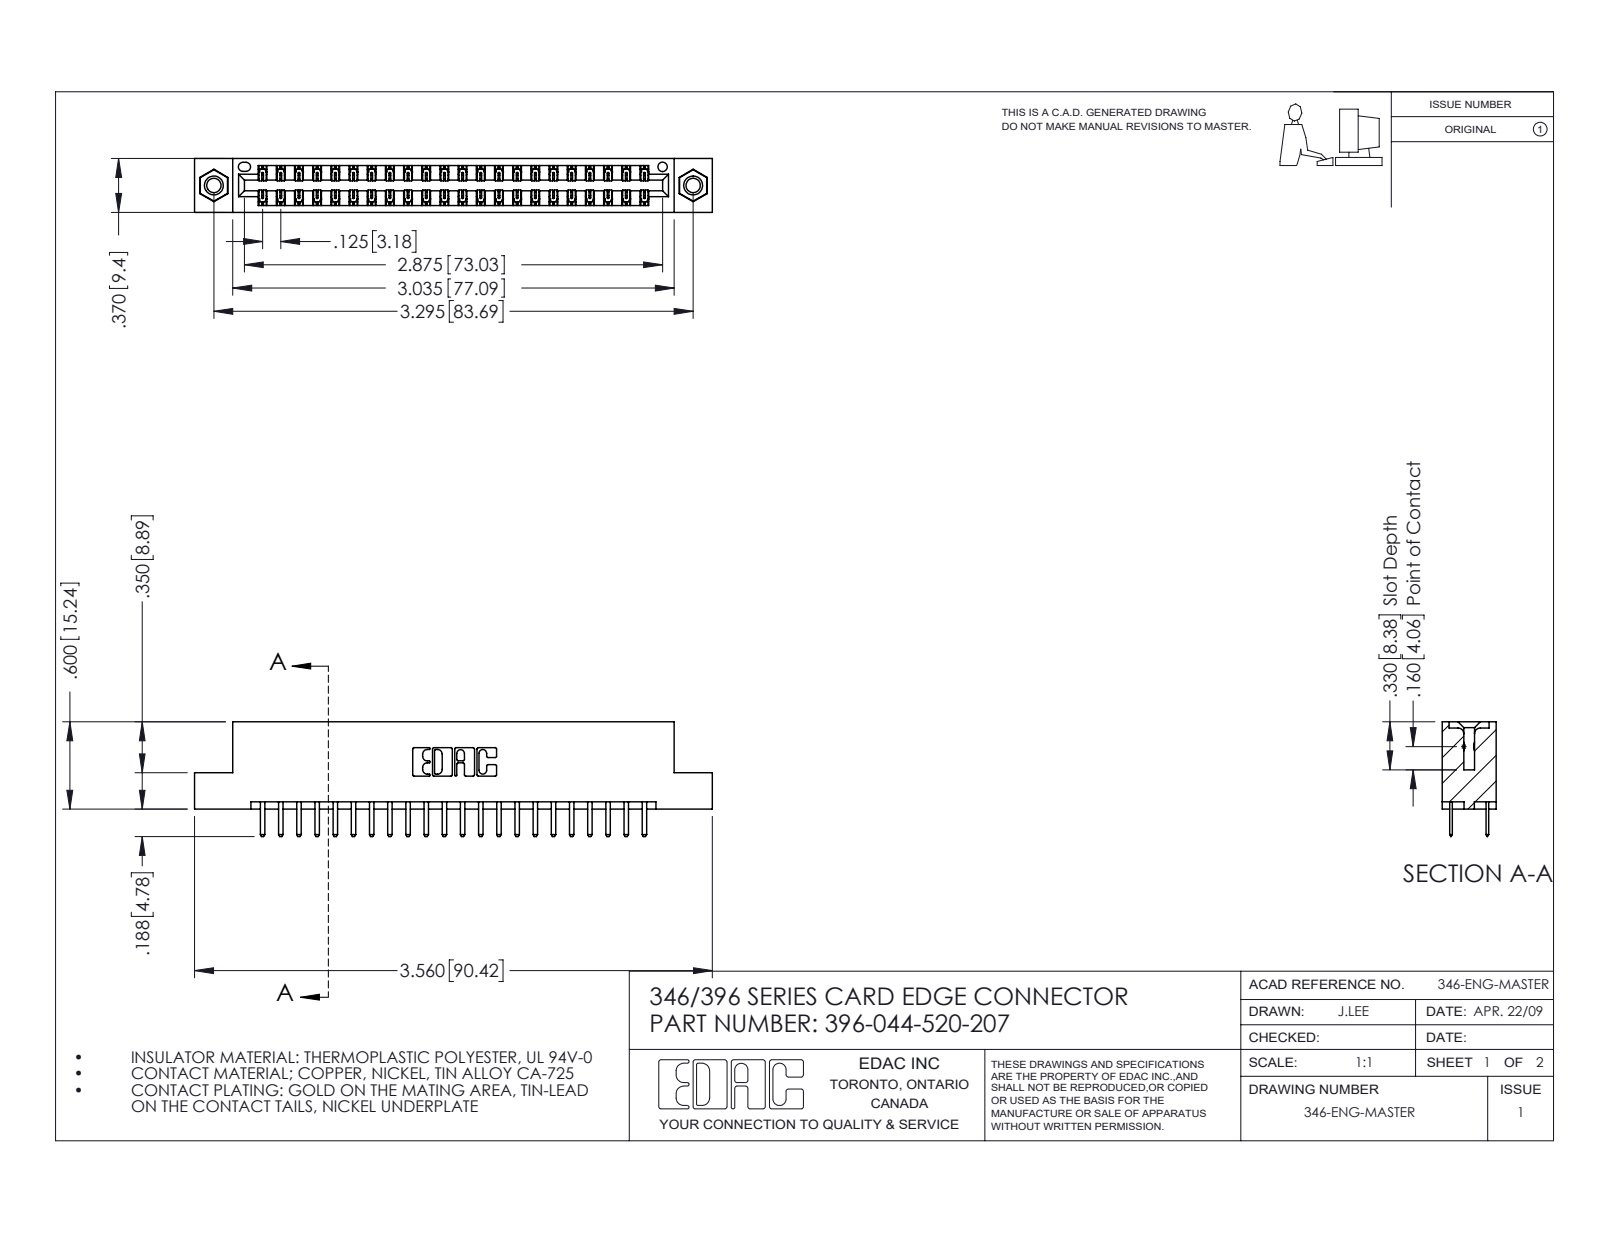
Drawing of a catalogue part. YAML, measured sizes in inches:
part_name: "396-044-520-207; 346 Part_Flush Mounting Lugs - 0.156 Dia-TI; 345-292-001_345-293-120; 345-250-001_345-250-005-103"
step_written_by: "SolidWorks 2016 (CONFIG_CONTROL_DESIGN)"
units: inches
bodies: {solids: 47, faces: 2646, planar: 1736, cylindrical: 894, other: 16}
overall_size: [3.56, 0.788, 0.37]
volume: 0.527
surface_area: 17.88
round_holes:
  - {diameter: 0.098, count: 2}
  - {diameter: 0.125, count: 2}
  - {diameter: 0.156, count: 2}
  - {diameter: 0.064, count: 1}
round_bosses_or_shafts:
  - {diameter: 0.155, count: 2}
partial_cylinders:
  - {radius: 0.006, count: 66}
  - {radius: 0.01, count: 48}
  - {radius: 0.01, count: 22}
  - {radius: 0.007, count: 6}
  - {radius: 0.031, count: 6}
  - {radius: 0.026, count: 3}
  - {radius: 0.014, count: 2}
  - {radius: 0.022, count: 2}
face_to_face_distances: [0.048, 0.322, 0.25, 0.37, 0.275, 0.072, 0.298, 0.025, 0.148, 0.222]
hole_center_spacings: [0.246, 3.087, 3.295]
